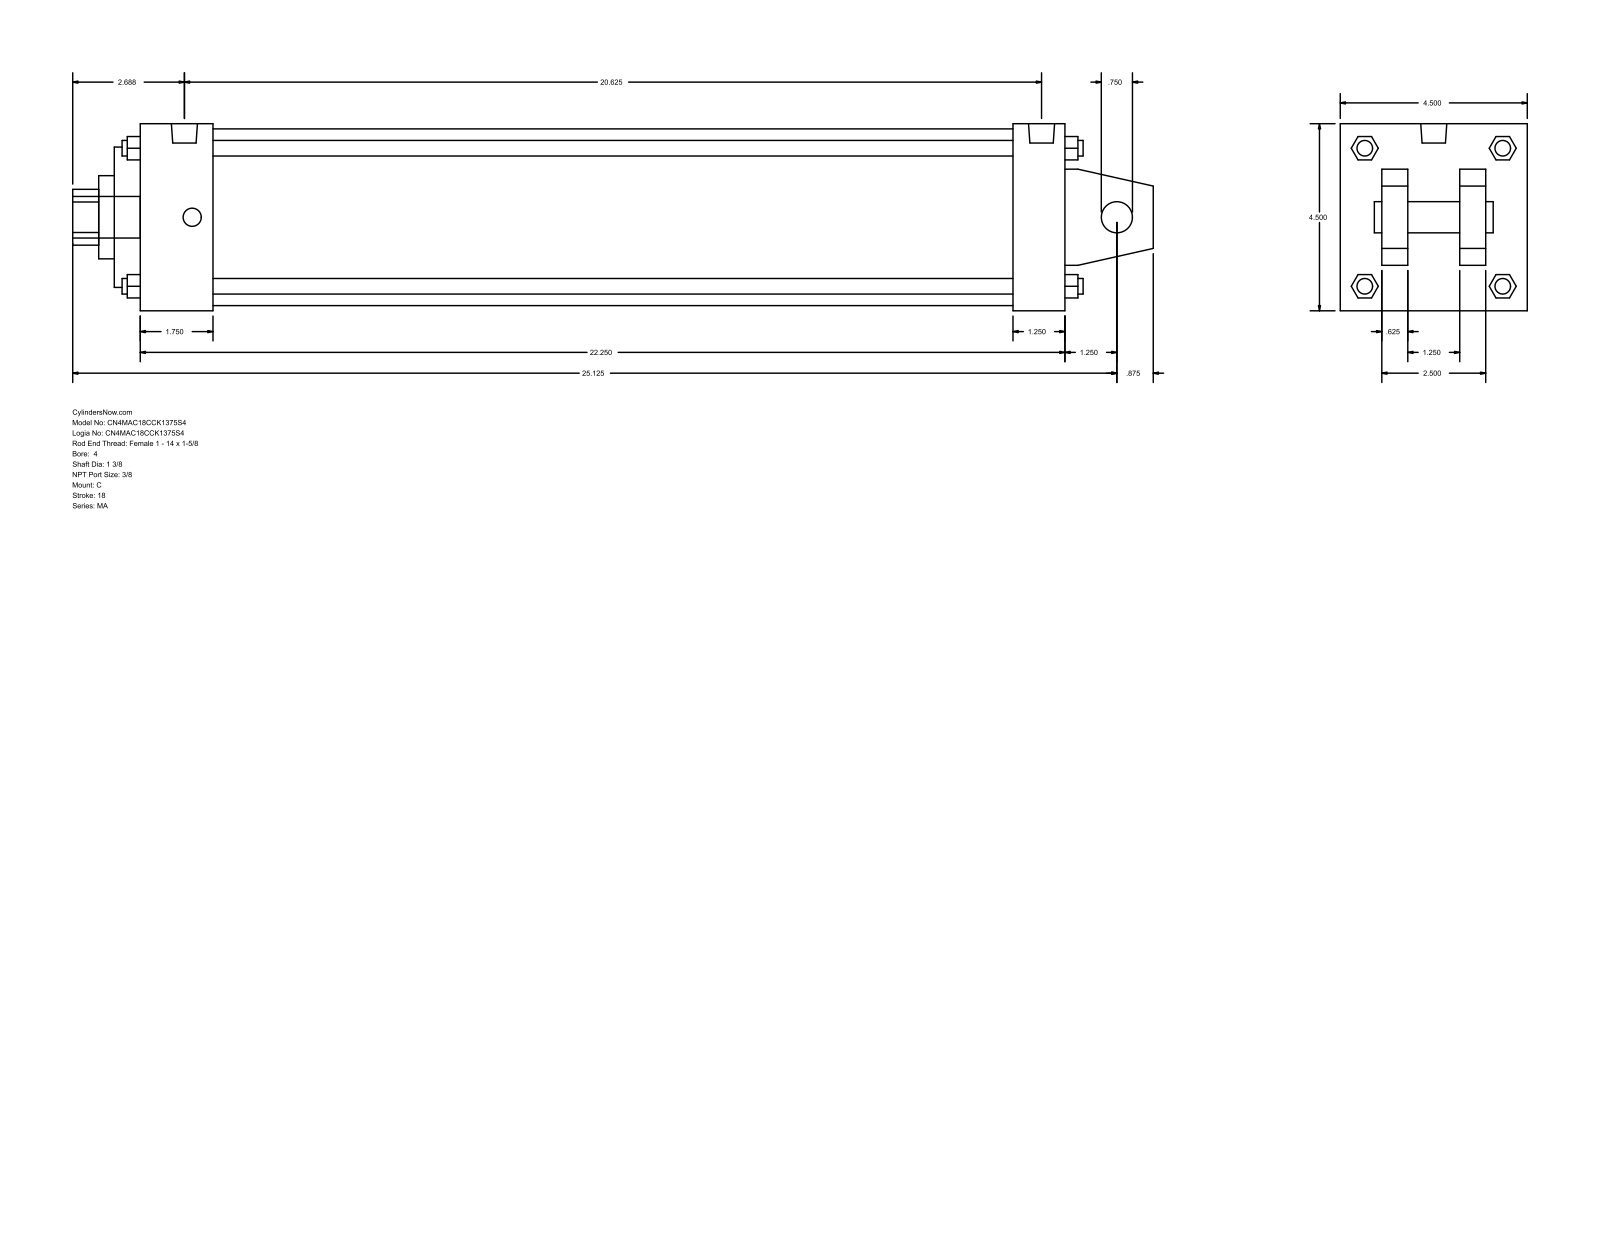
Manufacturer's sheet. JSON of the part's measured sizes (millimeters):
{"part_name": "MA_C__0400_1.375", "step_written_by": "GSSL Pune (CONFIG_CONTROL_DESIGN)", "units": "millimeters", "bodies": {"solids": 0, "faces": 141, "planar": 109, "cylindrical": 32, "other": 0}, "overall_size": [660.4, 114.3, 114.3], "round_holes": [[19.05, 1], [34.92, 1], [50.8, 1], [85.72, 1], [107.95, 1]], "round_bosses_or_shafts": [[11.11, 4], [9.53, 4], [15.93, 2], [25.4, 1]], "partial_cylinders_radius": [[17.06, 1]], "face_to_face_distances": [114.3, 15.87, 565.15, 73.03, 41.27, 25.4, 88.9, 47.63, 581.02, 549.27]}
